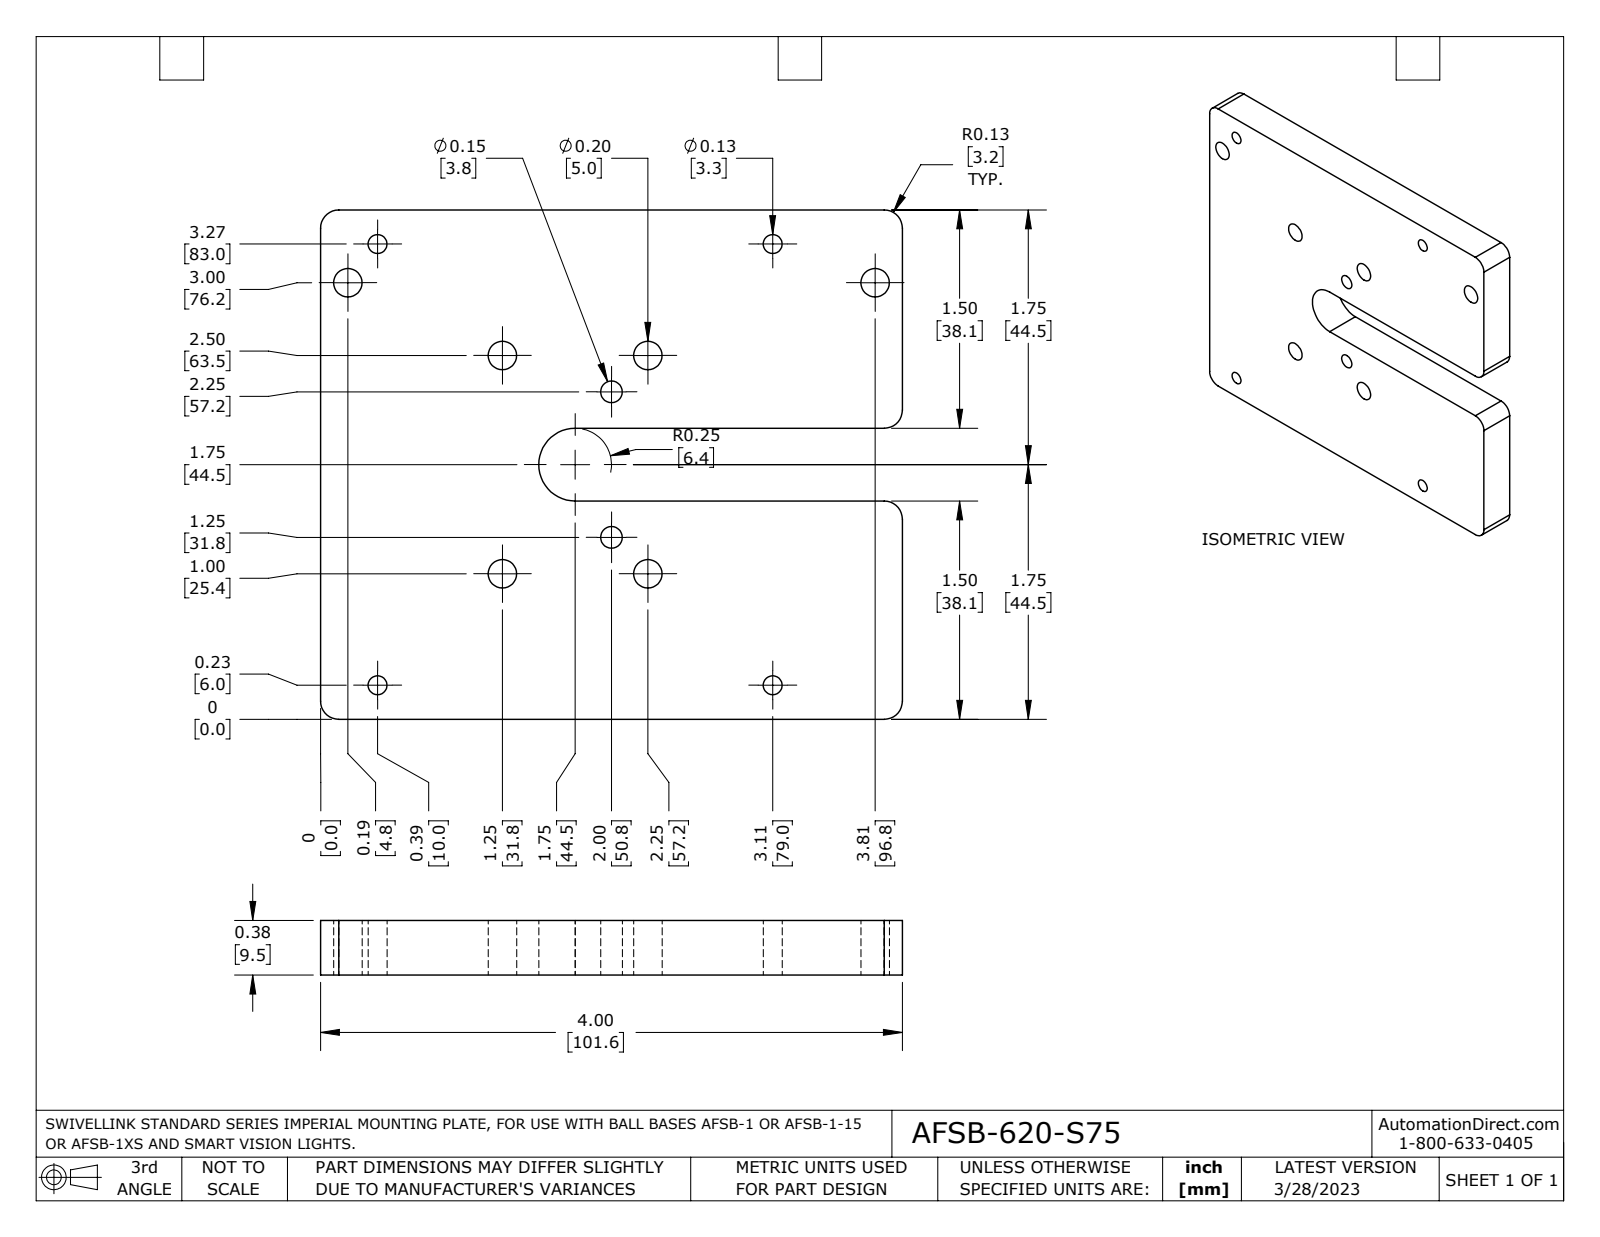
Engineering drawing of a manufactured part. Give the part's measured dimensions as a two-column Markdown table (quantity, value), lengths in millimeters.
| quantity | value |
| --- | --- |
| part name | AFSB-620-S75 |
| STEP written by | SolidWorks 2021 (AUTOMOTIVE_DESIGN) |
| units | millimeters |
| bodies | 1 solid, 28 faces (9 planar, 19 cylindrical, 0 other) |
| overall size | 101.6 × 88.9 × 9.5 |
| volume | 76 740 mm³ |
| surface area | 22 340 mm² |
| round holes (diameter × count) | 5 × 6, 3.3 × 4, 3.8 × 2 |
| partial cylindrical surfaces (radius × count) | 3.2 × 6, 6.4 × 1 |
| main face-to-face distances | 9.5, 38.1, 50.8, 88.9, 101.6, 12.7 |
| hole center spacings | 29.2, 51.1, 61.5, 74.4, 25.4, 9, 20.1, 32.4 |
